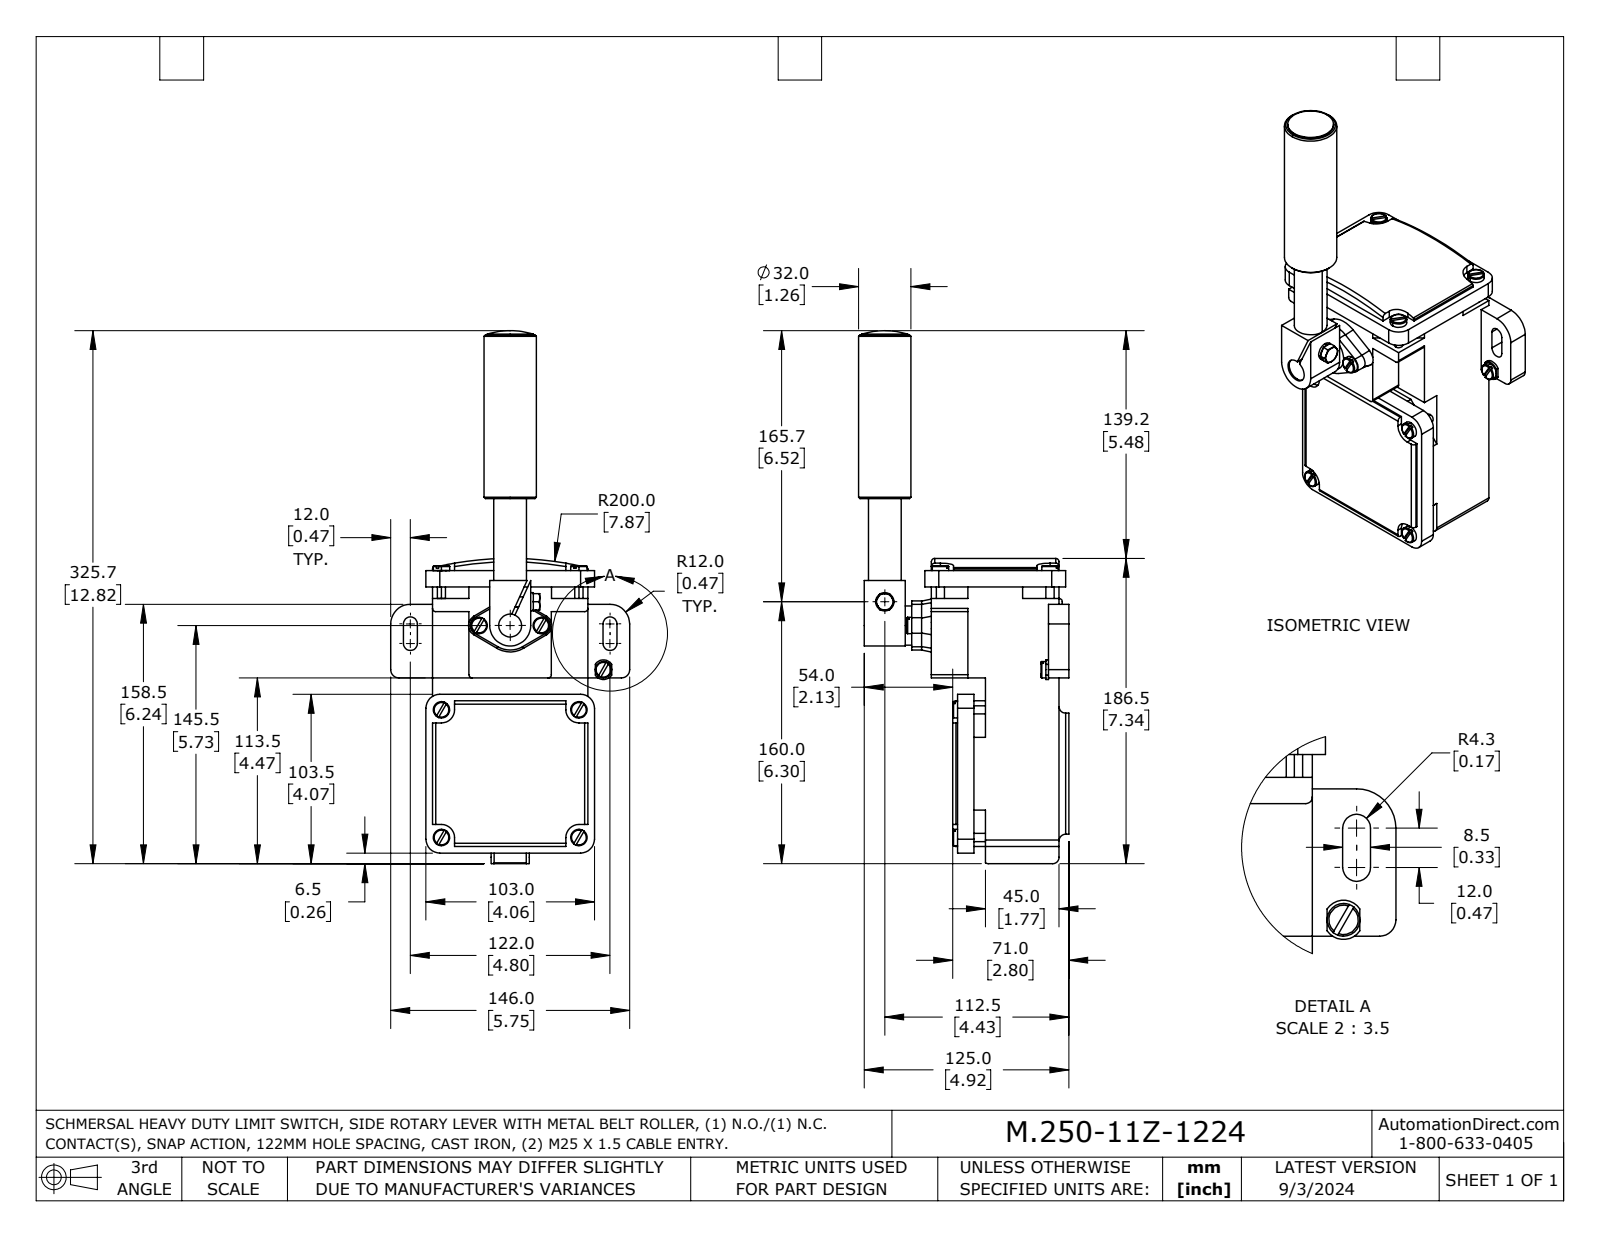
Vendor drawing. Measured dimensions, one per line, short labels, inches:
name: M.250-11Z-1224
written by: SolidWorks 2023 (AUTOMOTIVE_DESIGN)
unit: in
bodies: 2 solids, 360 faces (199 planar, 111 cylindrical, 50 other)
size: 12.821 × 5.748 × 5.059
volume: 79.93 in³; area: 188.6 in²
holes: 1× ⌀0.262, 1× ⌀0.92
bosses: 11× ⌀0.394, 8× ⌀0.197, 1× ⌀2.913, 1× ⌀1.26, 1× ⌀1.102, 1× ⌀0.945, 1× ⌀0.787, 1× ⌀0.551
rounds: 8× R0.079, 8× R0.315, 8× R0.335, 4× R0.157, 4× R0.167, 2× R0.039, 2× R0.197, 2× R0.217
face distances: 2.559, 3.74, 0.157, 0.236, 2.795, 0.512, 0.394, 0.787, 4.055, 2.185
hole spacings: 5.753
